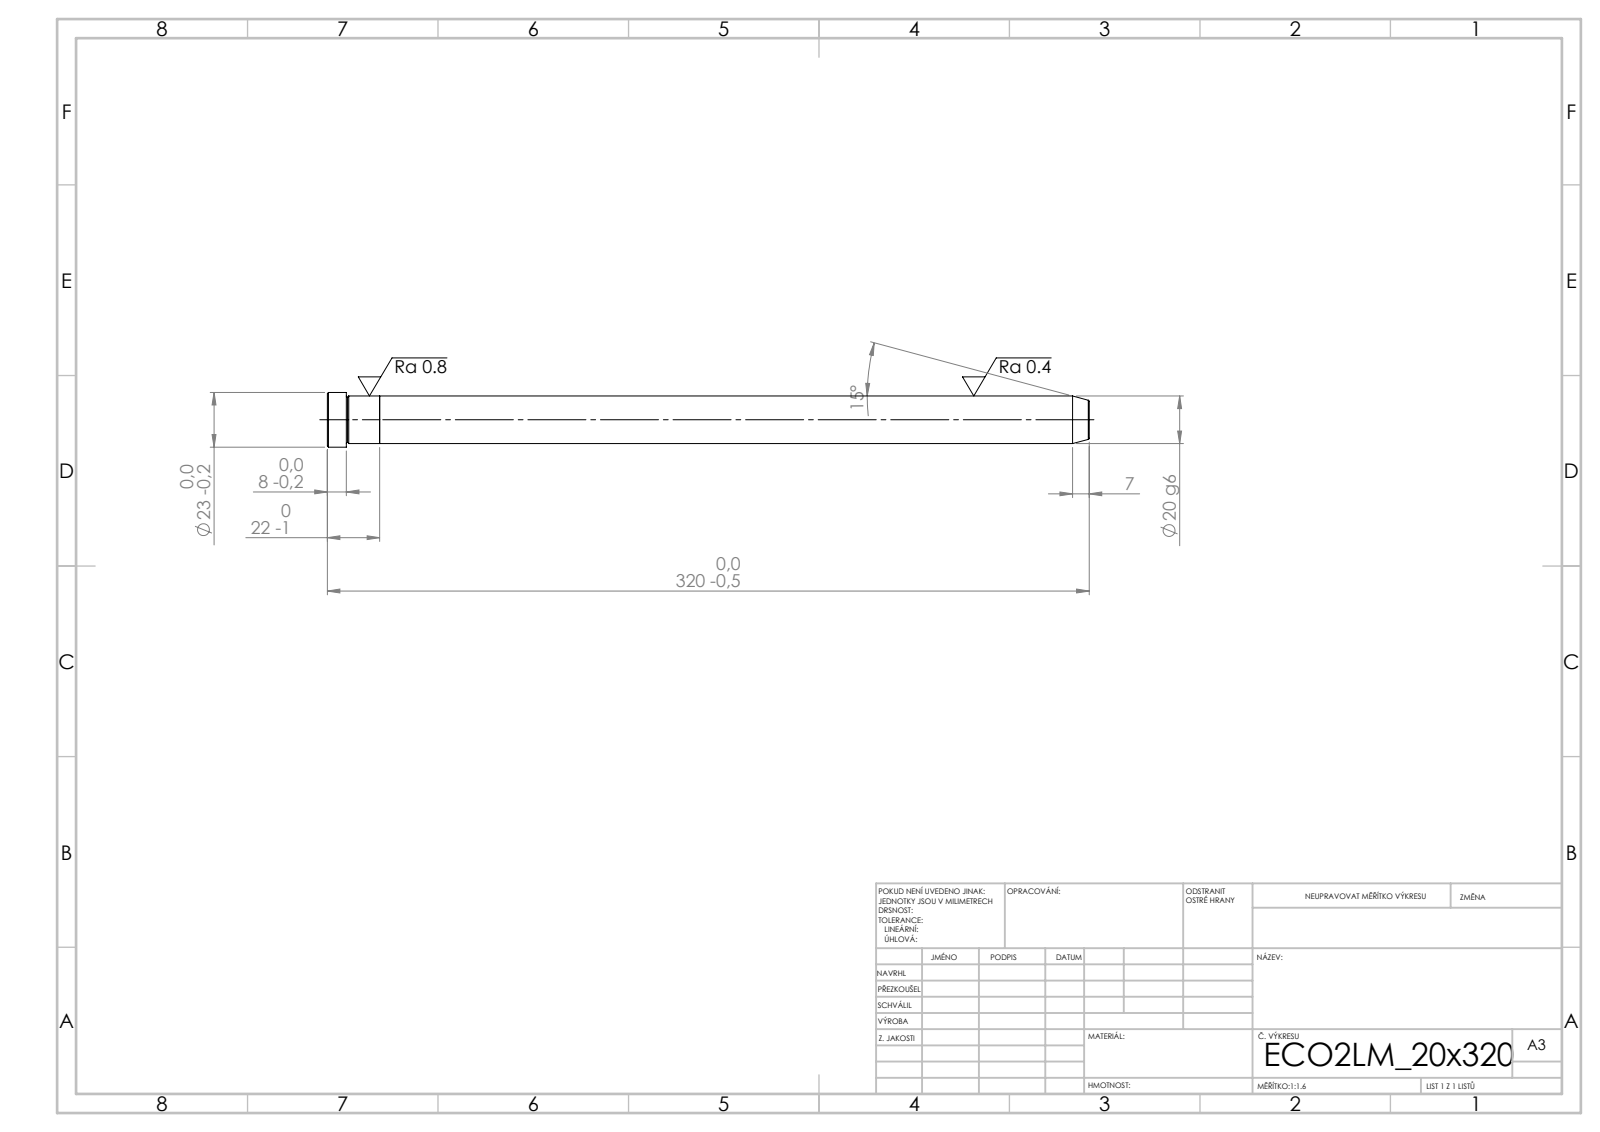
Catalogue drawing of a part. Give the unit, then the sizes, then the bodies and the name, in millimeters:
Units: millimetres
Overall size (bounding box): 320 × 23 × 23
Round bosses / shafts (diameter × count): ⌀23 ×1, ⌀20 ×1
Main face-to-face distances: 22, 298, 320, 312, 14, 8
Volume: 100 920 mm³ · Surface area: 21 512 mm²
Bodies: 2 solids, 21 faces (5 planar, 6 cylindrical, 10 other)
STEP written by: SolidWorks 2019 (CONFIG_CONTROL_DESIGN)
